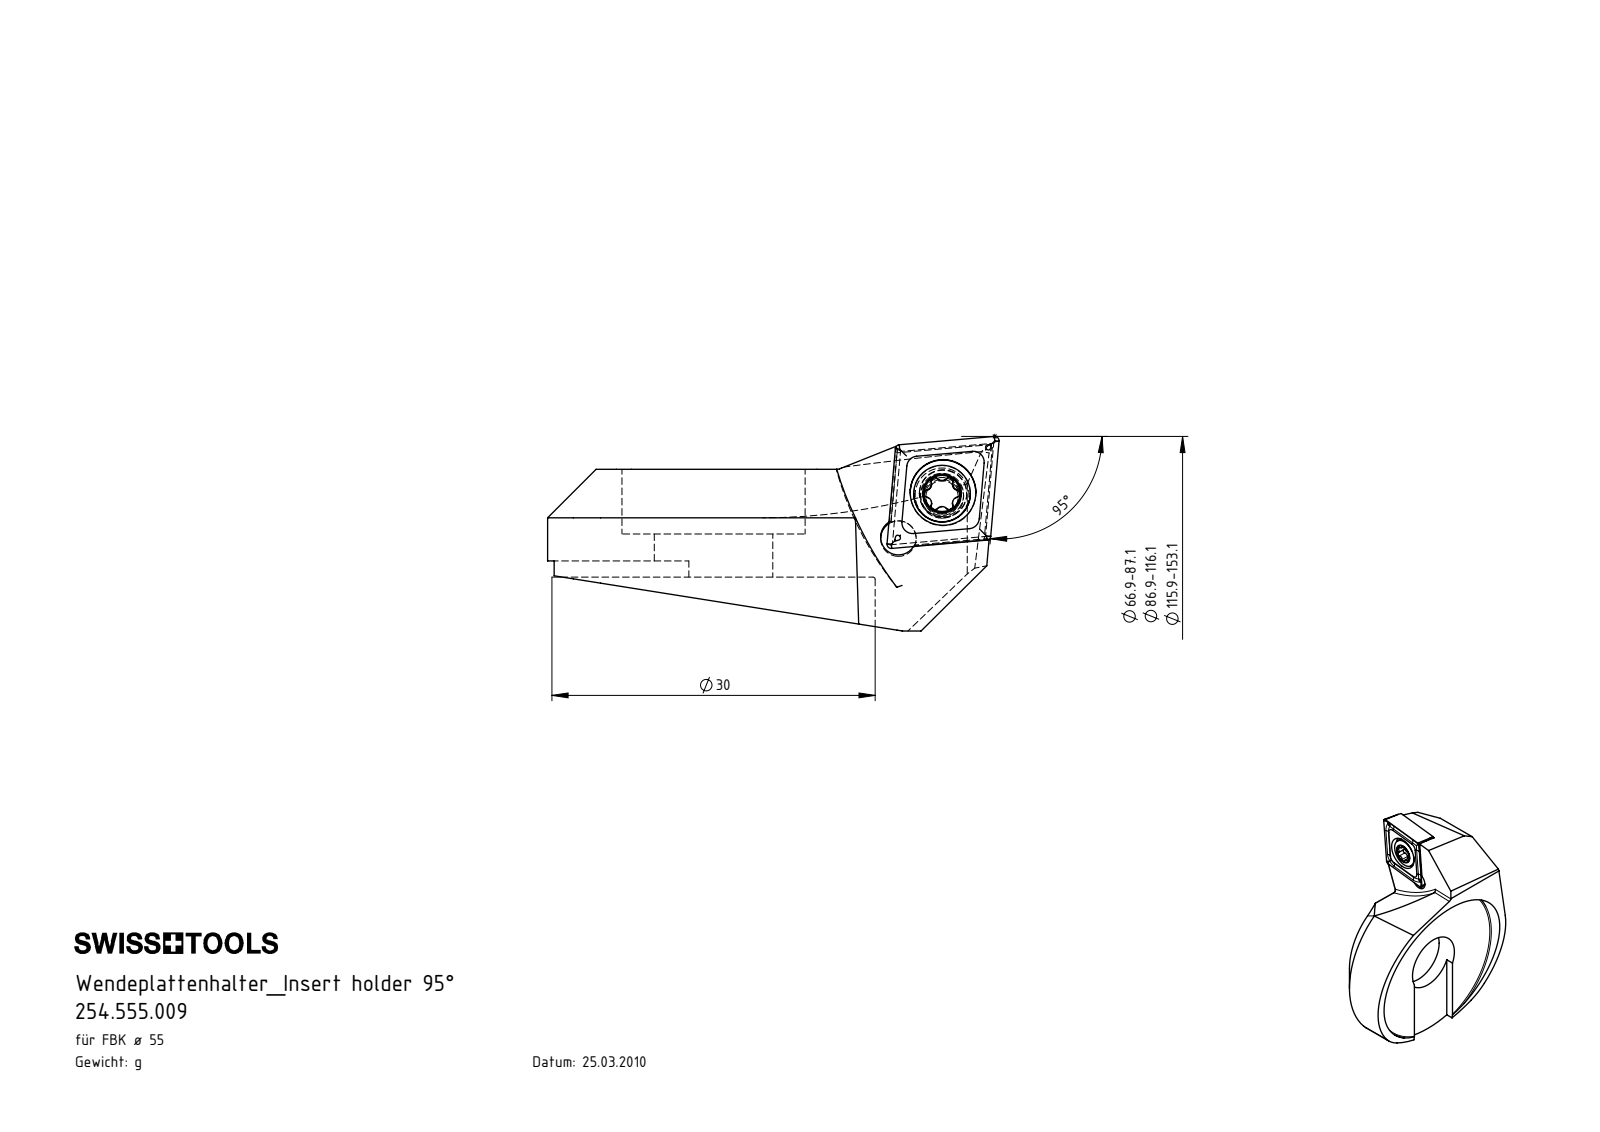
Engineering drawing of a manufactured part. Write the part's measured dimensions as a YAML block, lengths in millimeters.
part_name: "CCMT09T304; F55-WCB.002.013_D_fertigbearbeitet; WCB-ER2.001.009_A; 254.555.009"
step_written_by: "SolidWorks 2017 (CONFIG_CONTROL_DESIGN)"
units: millimeters
bodies: {solids: 5, faces: 156, planar: 50, cylindrical: 46, other: 60}
overall_size: [41.9, 33.1, 18.05]
volume: 8191
surface_area: 5039
round_holes:
  - {diameter: 3.3, count: 2}
  - {diameter: 4.4, count: 1}
  - {diameter: 6.1, count: 1}
  - {diameter: 11, count: 1}
  - {diameter: 17, count: 1}
  - {diameter: 30, count: 1}
round_bosses_or_shafts:
  - {diameter: 5.25, count: 1}
  - {diameter: 4, count: 1}
partial_cylinders:
  - {radius: 0.34, count: 6}
  - {radius: 0.59, count: 6}
  - {radius: 0.5, count: 2}
  - {radius: 10, count: 2}
  - {radius: 1.65, count: 1}
  - {radius: 16.55, count: 1}
  - {radius: 20.9, count: 1}
  - {radius: 30, count: 1}
face_to_face_distances: [10, 9, 1, 3.77, 5, 6, 4, 8.5, 7.5, 2.5]
hole_center_spacings: [5.73, 5.86]
